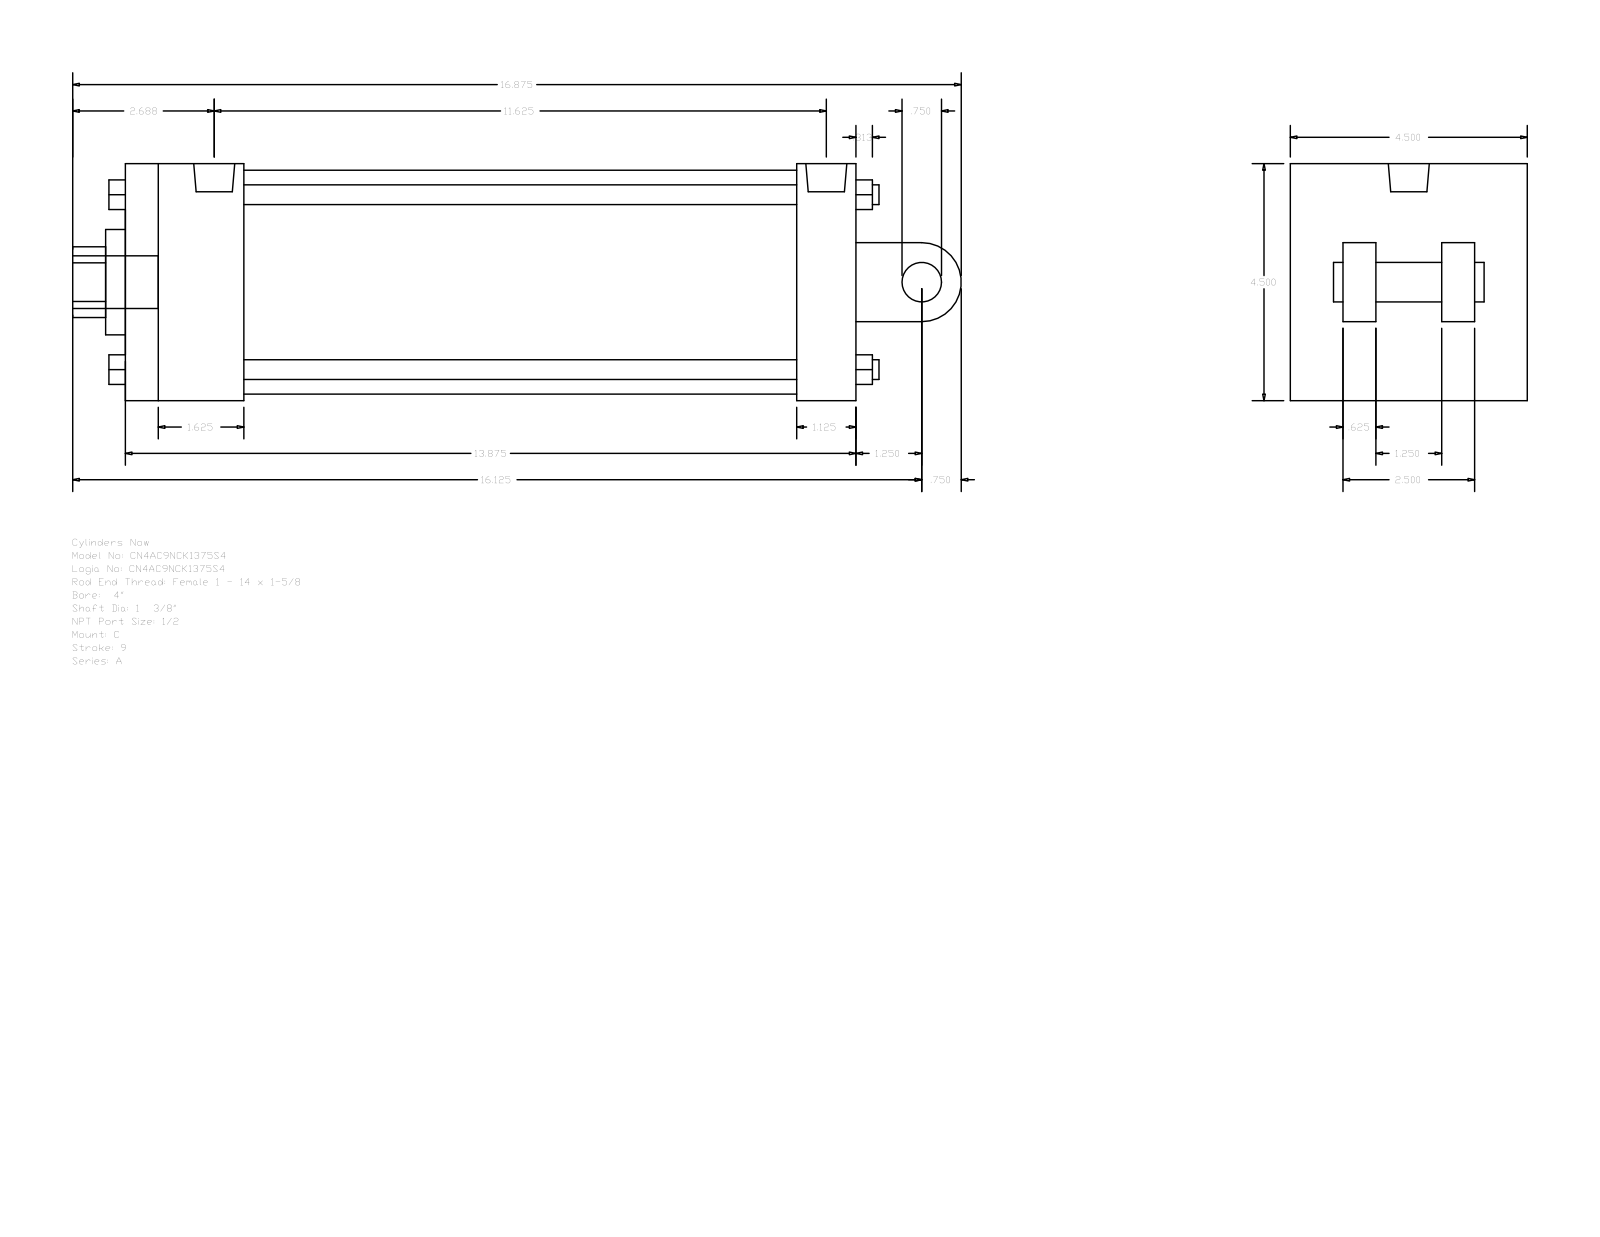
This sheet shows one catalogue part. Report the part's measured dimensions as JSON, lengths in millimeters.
{"part_name": "A_C__0400_1.375", "step_written_by": "GSSL Pune (CONFIG_CONTROL_DESIGN)", "units": "millimeters", "bodies": {"solids": 0, "faces": 135, "planar": 102, "cylindrical": 33, "other": 0}, "overall_size": [428.62, 114.3, 114.3], "round_holes": [[8.73, 2], [19.77, 1], [34.92, 1], [50.8, 1], [107.95, 1]], "round_bosses_or_shafts": [[9.53, 4], [8.73, 2], [25.4, 1], [19.77, 1], [19.05, 1]], "partial_cylinders_radius": [[17.06, 1], [19.05, 1]], "face_to_face_distances": [114.3, 352.42, 73.03, 28.57, 323.85, 57.15, 266.7, 295.27, 15.87, 41.27], "hole_center_spacings": [3.18]}
